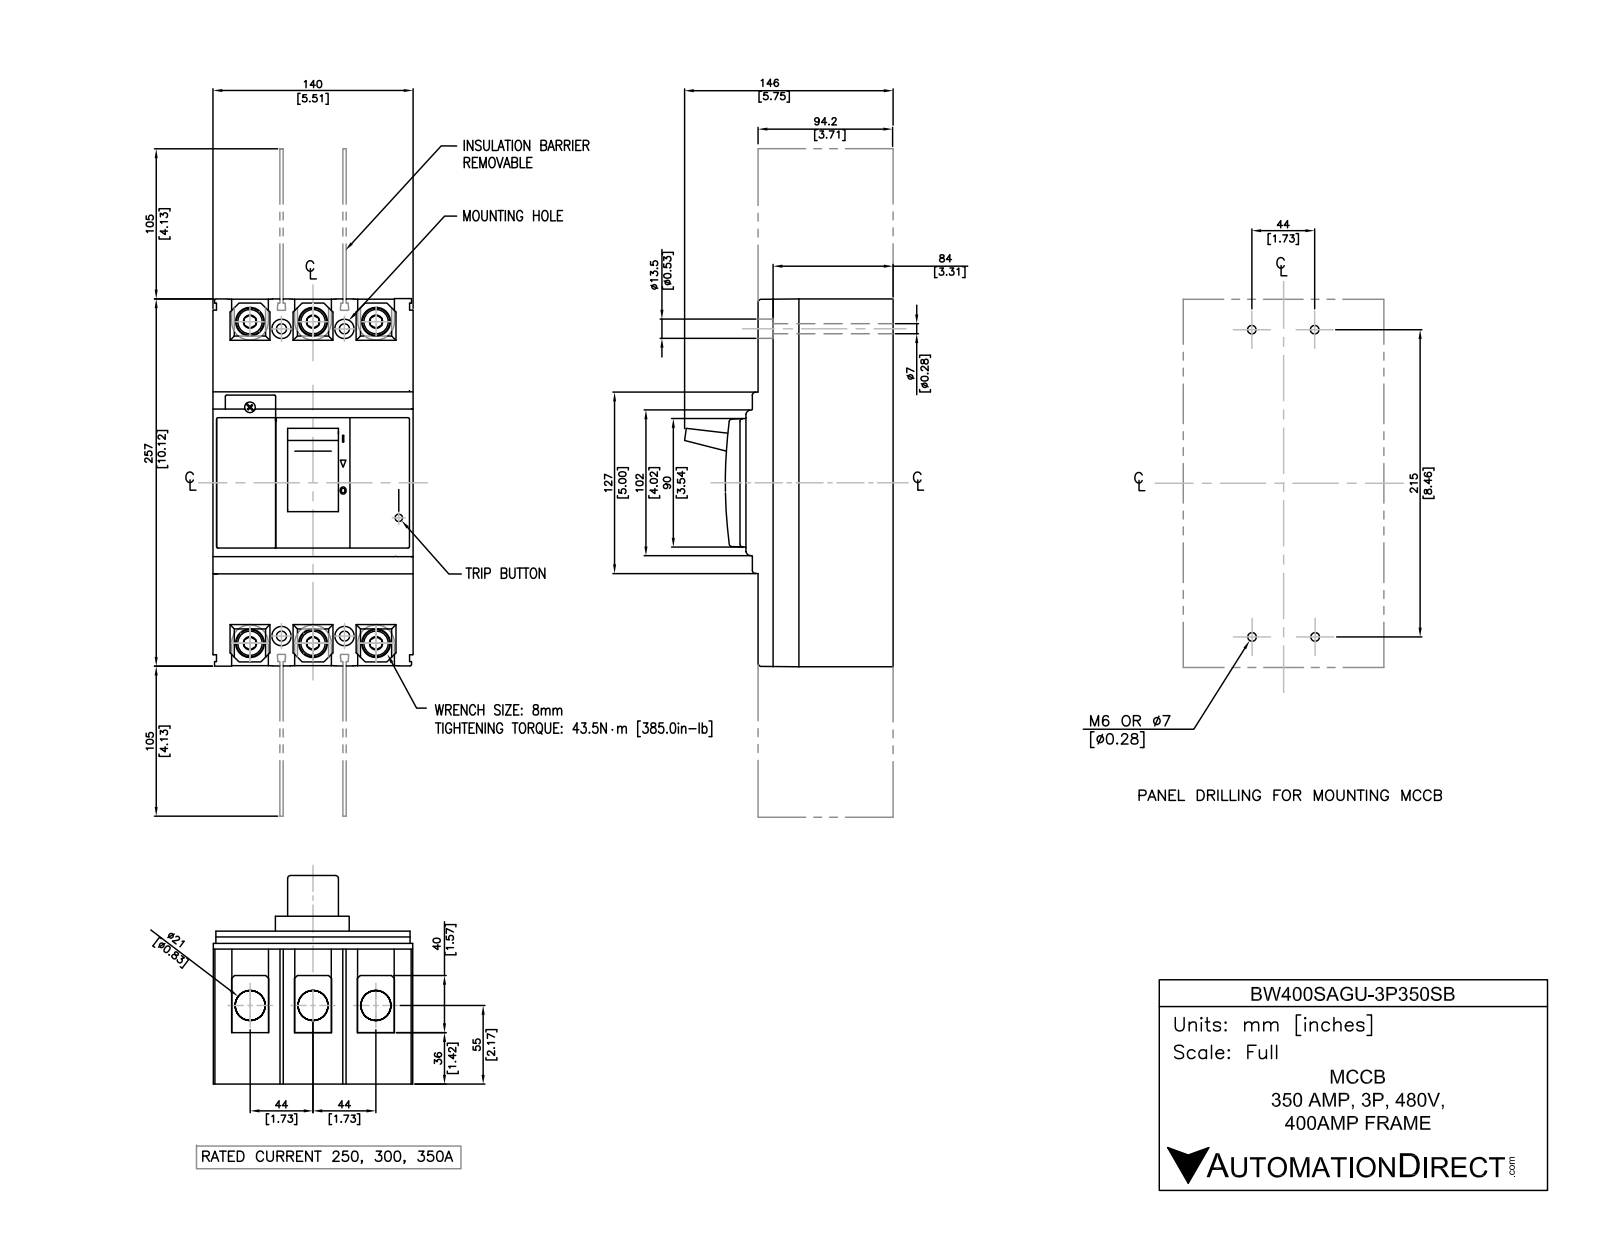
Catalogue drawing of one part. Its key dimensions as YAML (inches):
part_name: "BW400SAGU-3P350SB"
step_written_by: "SolidWorks 2018 (AUTOMOTIVE_DESIGN)"
units: inches
bodies: {solids: 18, faces: 382, planar: 320, cylindrical: 62, other: 0}
overall_size: [13.386, 5.839, 5.512]
volume: 205.5
surface_area: 392.8
round_holes:
  - {diameter: 0.276, count: 4}
  - {diameter: 0.413, count: 4}
  - {diameter: 0.472, count: 4}
  - {diameter: 0.492, count: 4}
  - {diameter: 0.531, count: 4}
round_bosses_or_shafts:
  - {diameter: 0.394, count: 4}
partial_cylinders:
  - {radius: 0.504, count: 6}
face_to_face_distances: [5.512, 1.732, 0.315, 3.72, 1.26, 2.303, 1.417, 0.394, 1.988, 0.492]
hole_center_spacings: [0.888, 1.691, 2.267, 2.606, 3.584, 4.275, 8.705, 9.043]
